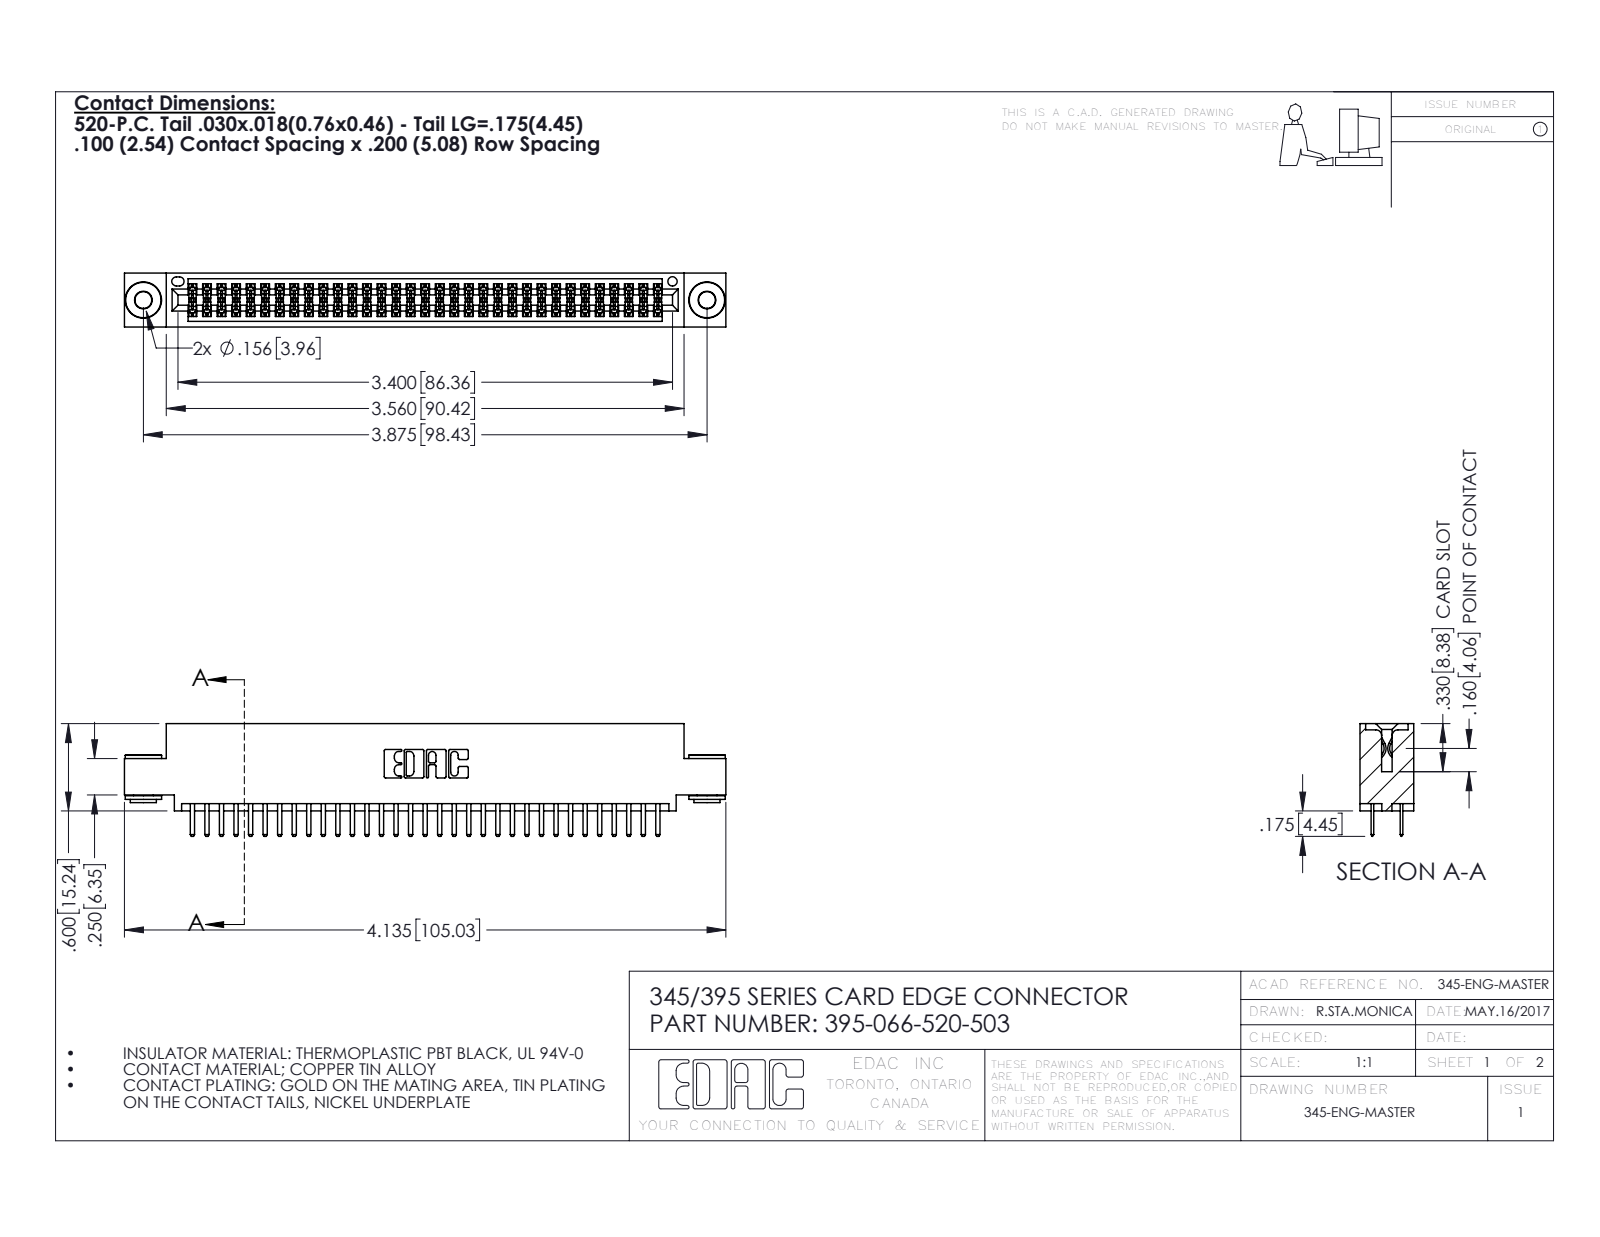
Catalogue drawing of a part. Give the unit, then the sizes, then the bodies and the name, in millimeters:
Units: millimetres
Overall size (bounding box): 105 × 19.7 × 9.4
Round holes (diameter × count): ⌀2.9 ×2, ⌀4 ×2, ⌀1.6 ×1
Round bosses / shafts (diameter × count): ⌀6.4 ×2, ⌀4.6 ×2, ⌀3.5 ×2
Partial cylindrical surfaces — rounded edges, fillets, slot ends (radius × count): R0.2 ×99, R0.3 ×70, R0.3 ×22, R0.2 ×6, R0.8 ×6, R0.7 ×3, R0.4 ×2, R0.5 ×2
Main face-to-face distances: 1.8, 7.6, 5.1, 9.4, 0.6, 2.5, 6.9, 5.7, 0.6, 1.8
Hole centre spacings: 6.9, 92.5, 98.4
Volume: 10 000 mm³ · Surface area: 14 900 mm²
Bodies: 69 solids, 3732 faces (2404 planar, 1320 cylindrical, 8 other)
Part name (STEP PRODUCT): 345 Part_0.110 Offset - 0.156 Dia-TH; 345-292-001_345-293-120; 345-250-002_345-250-002-102; 395-066-520-503
STEP written by: SolidWorks 2016 (CONFIG_CONTROL_DESIGN)
